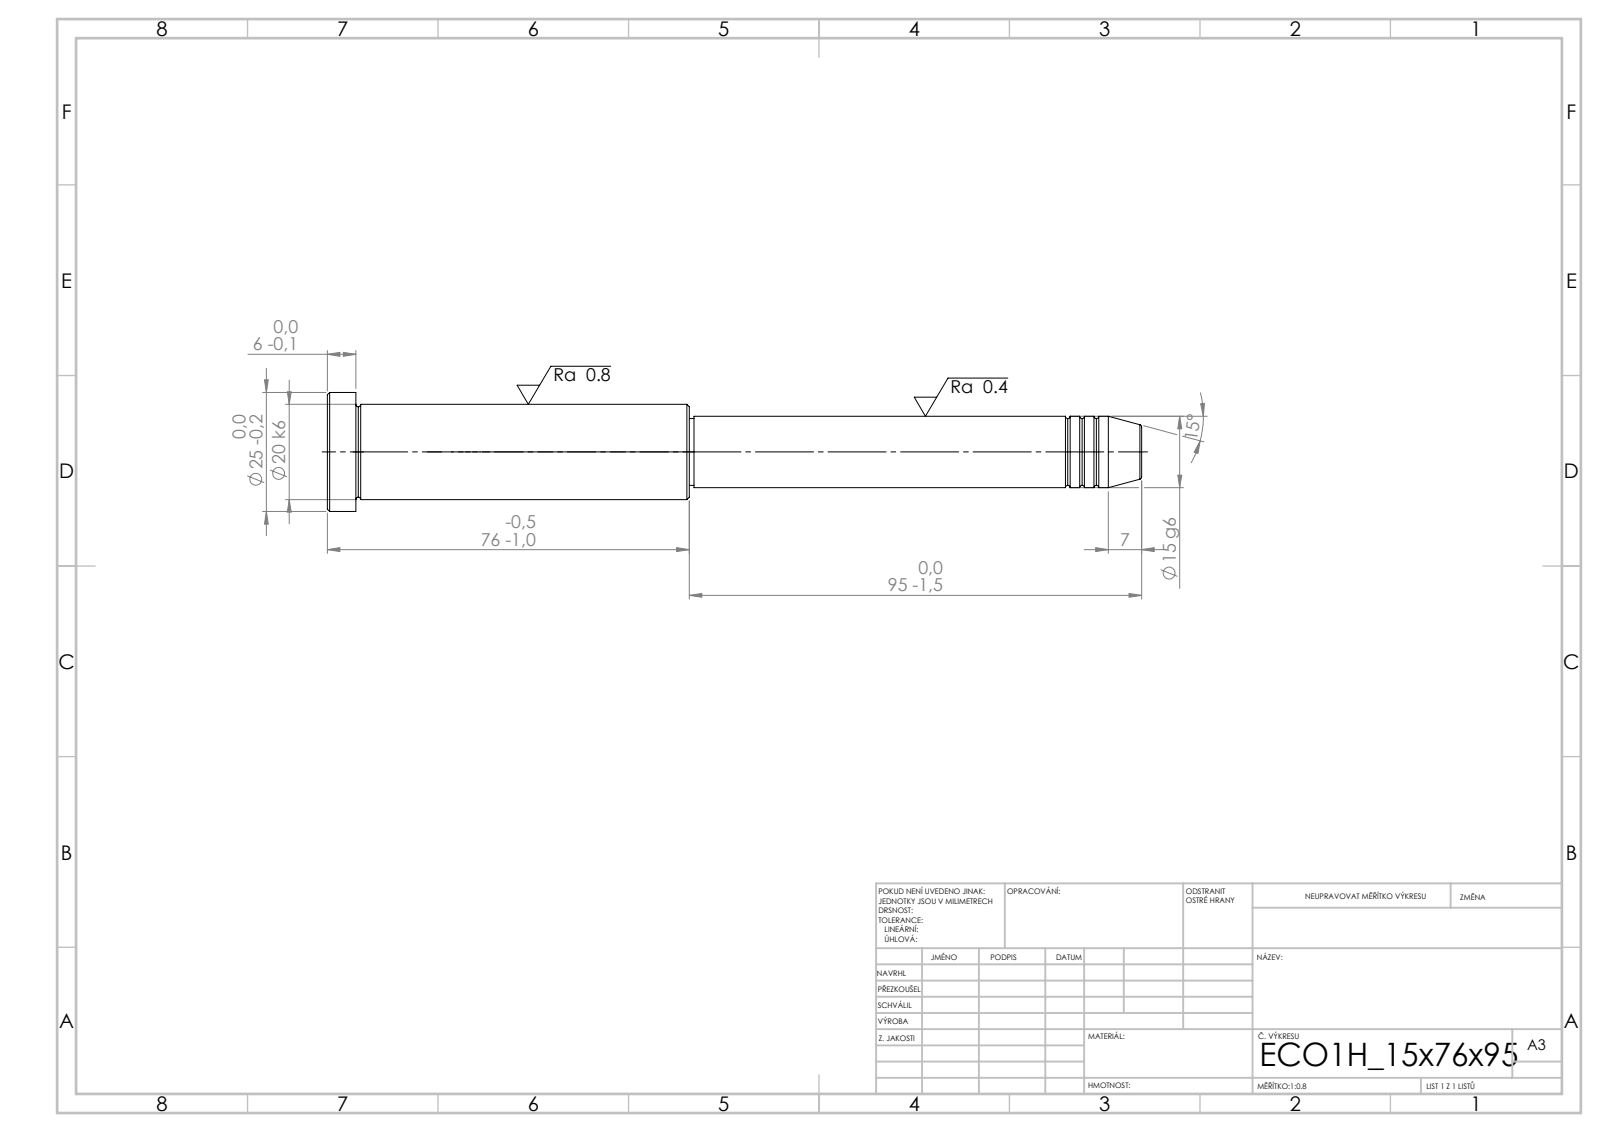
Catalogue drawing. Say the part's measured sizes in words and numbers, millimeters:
Its 3-D file was written by "SolidWorks 2019 (CONFIG_CONTROL_DESIGN)". It is 1 solid with 43 faces: 5 planar, 14 cylindrical and 24 other. Overall it measures 171 by 25 by 25 millimeters. Its volume is 41 321 cubic millimeters and its surface area 10 320 square millimeters. Round bosses or shafts: 1 of diameter 25, 1 of diameter 20, 1 of diameter 15, 1 of diameter 14. The main face-to-face distances are 6, 70, 76, 95, 165, 171, 94, 1, 71, 77.
